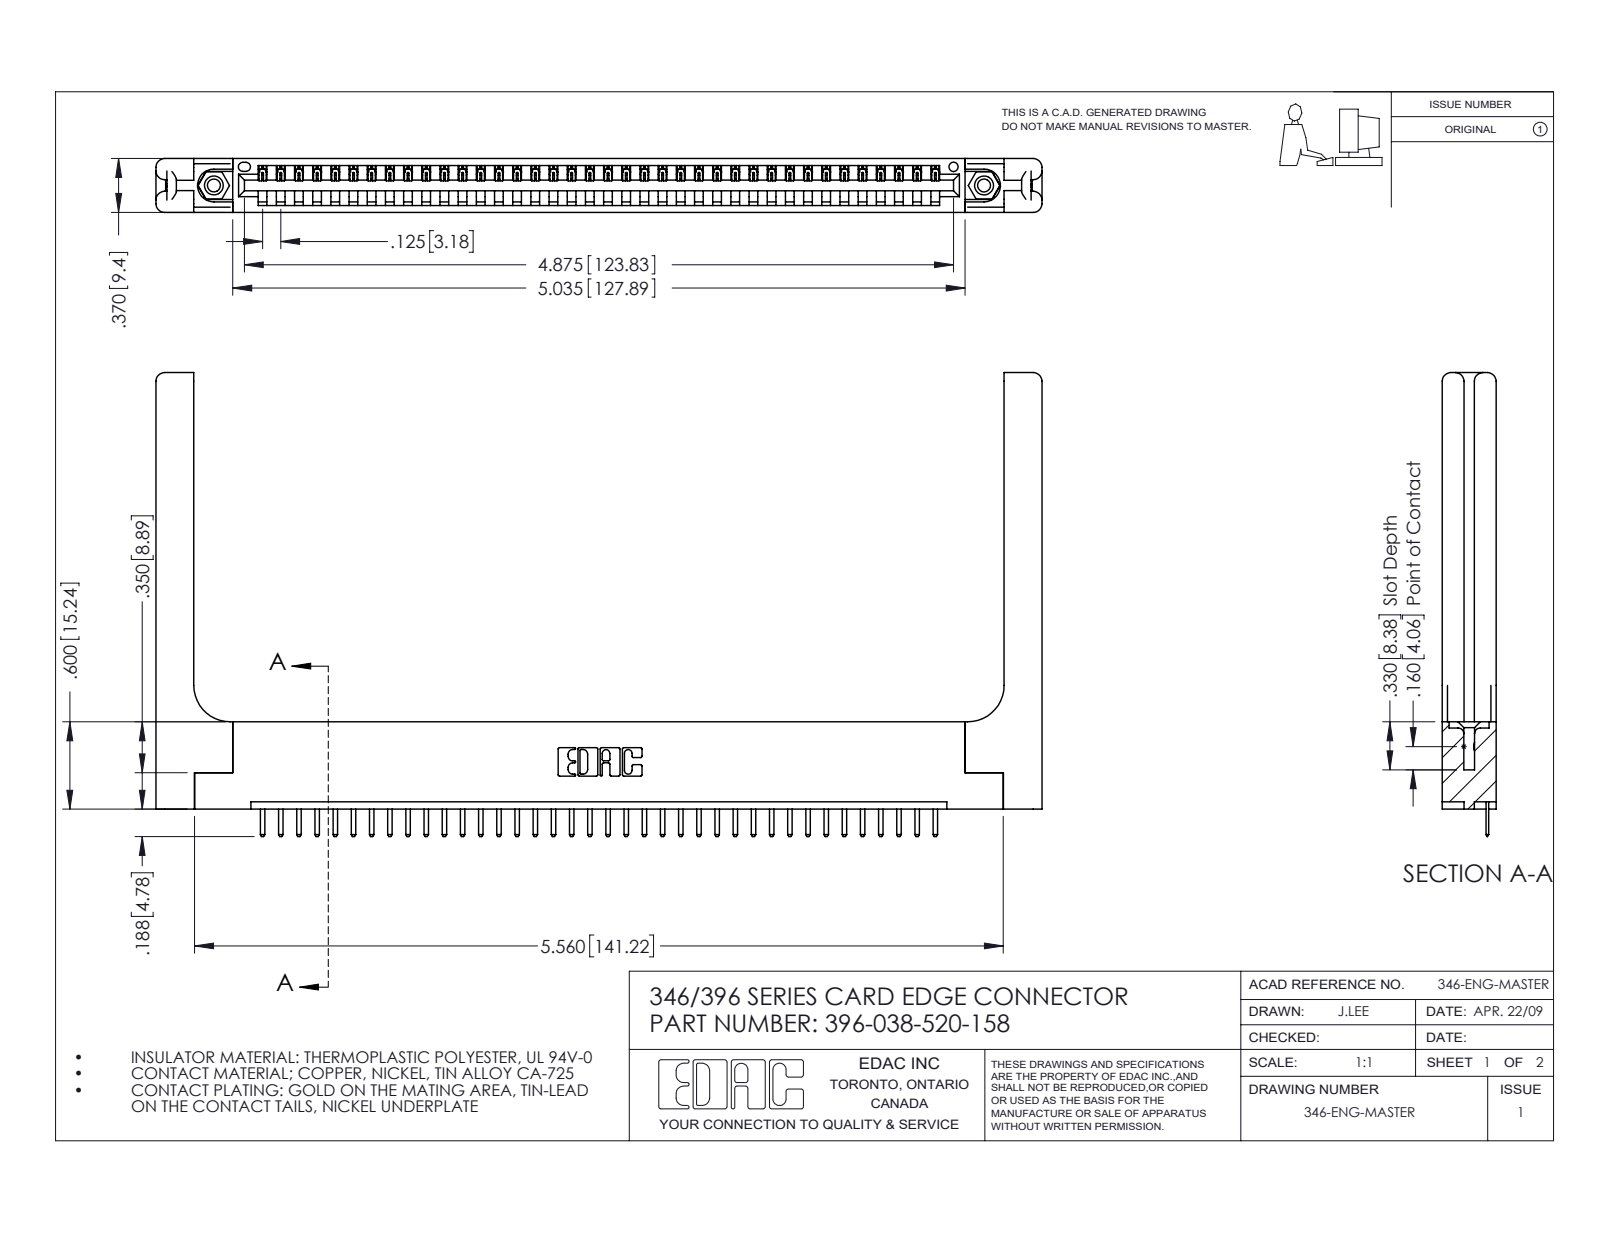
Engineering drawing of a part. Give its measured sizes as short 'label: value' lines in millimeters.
name: 346 Part_Flush Mounting Lugs - 0.156 Dia-TH; 346-220-058_345-220-058; 396-038-520-158; 345-250-001_345-250-001-102 (+1 more)
written by: SolidWorks 2016 (CONFIG_CONTROL_DESIGN)
unit: mm
bodies: 43 solids, 2734 faces (1820 planar, 854 cylindrical, 60 other)
size: 154.7 × 81 × 9.4
volume: 22 190 mm³; area: 23 100 mm²
holes: 2× ⌀2.3, 2× ⌀3.2, 2× ⌀4, 1× ⌀1.6
bosses: 2× ⌀3.9
rounds: 78× R0.3, 76× R0.2, 22× R0.3, 16× R1.5, 6× R0.2, 6× R0.8, 3× R0.7, 2× R0.8
face distances: 9.4, 1.2, 8.2, 1.8, 3.8, 3.8, 6.4, 7.6, 0.6, 5.6
hole spacings: 6.2, 129.2, 134.5
